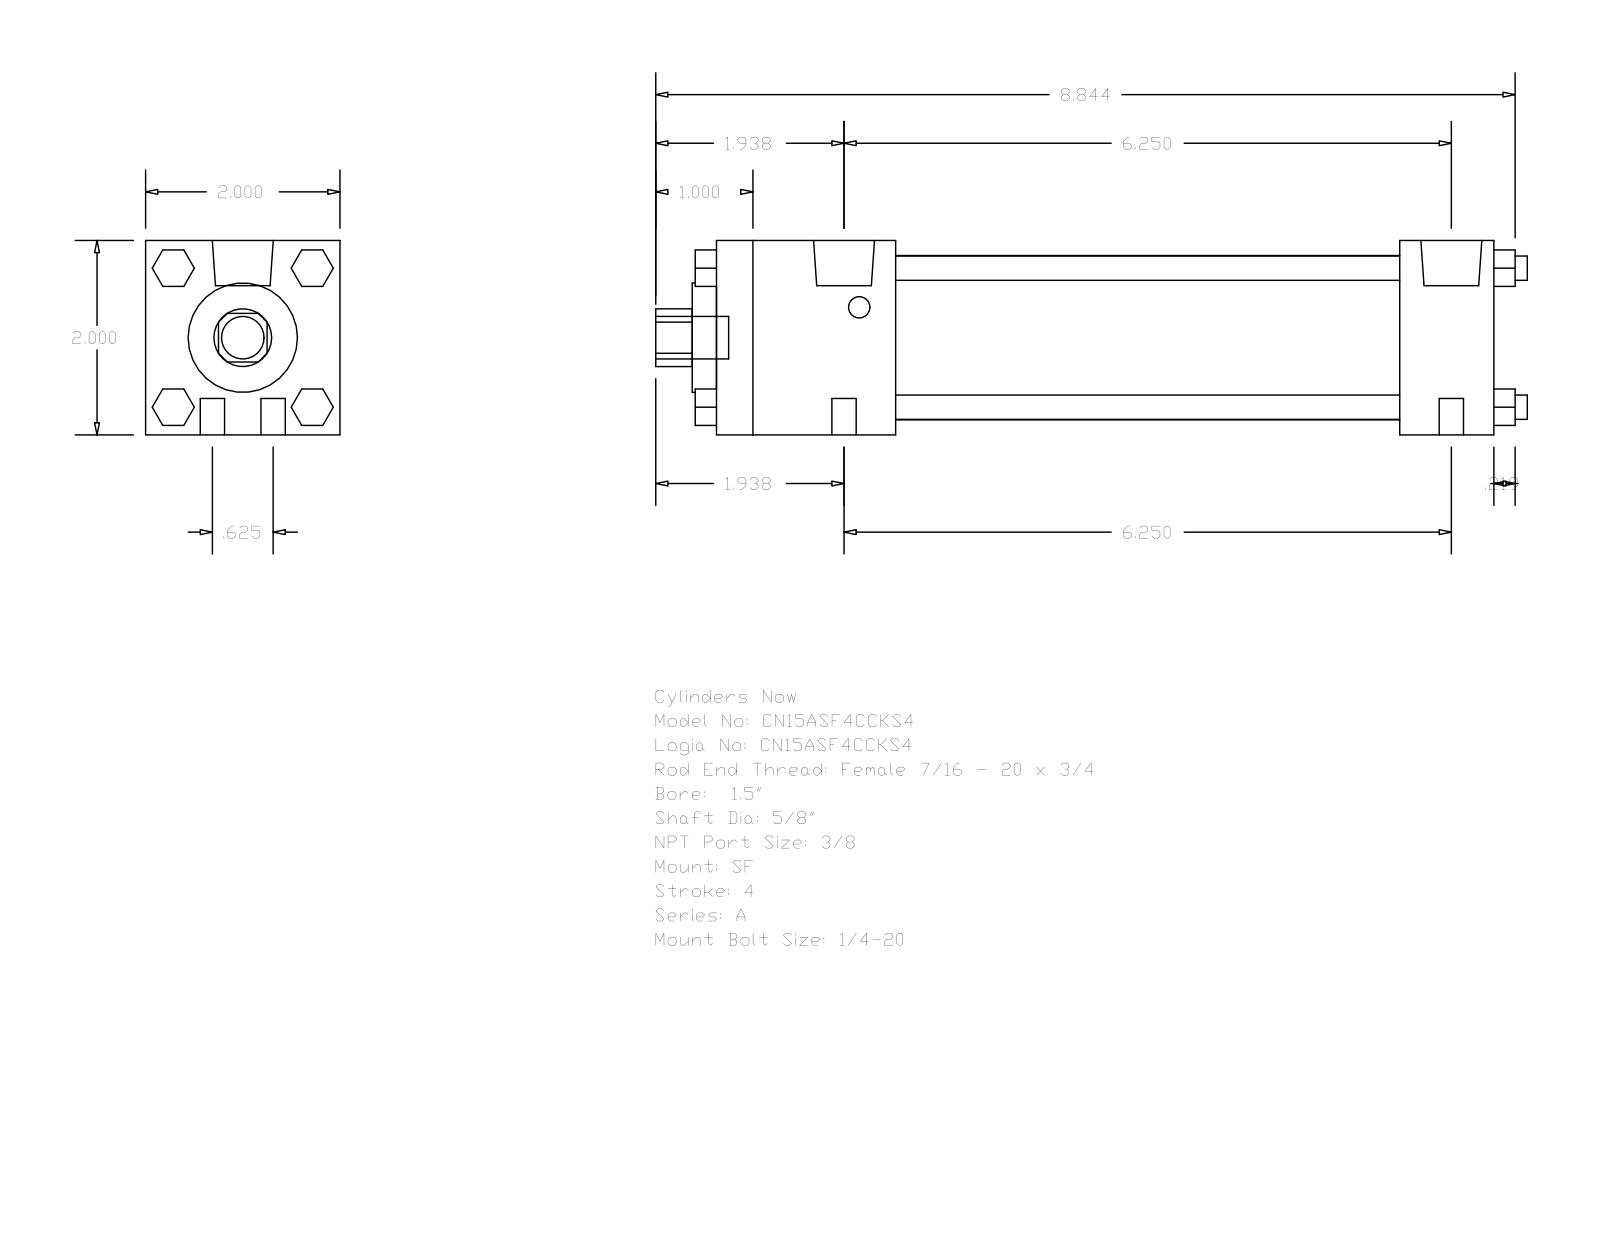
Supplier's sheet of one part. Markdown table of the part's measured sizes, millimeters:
| quantity | value |
| --- | --- |
| part name | A_SF__0150_0.625 |
| STEP written by | GSSL Pune (CONFIG_CONTROL_DESIGN) |
| units | millimeters |
| bodies | 0 solids, 124 faces (94 planar, 30 cylindrical, 0 other) |
| overall size | 227.81 × 50.8 × 50.8 |
| round holes (diameter × count) | 15.88 × 1, 28.57 × 1, 42.93 × 1 |
| round bosses / shafts (diameter × count) | 6.35 × 8, 15.93 × 2, 5.56 × 2, 11.11 × 1 |
| partial cylindrical surfaces (radius × count) | 7.54 × 1 |
| main face-to-face distances | 50.8, 203.19, 46.83, 178.59, 131.76, 156.36, 24.6, 9.52, 6.35, 53.18 |
